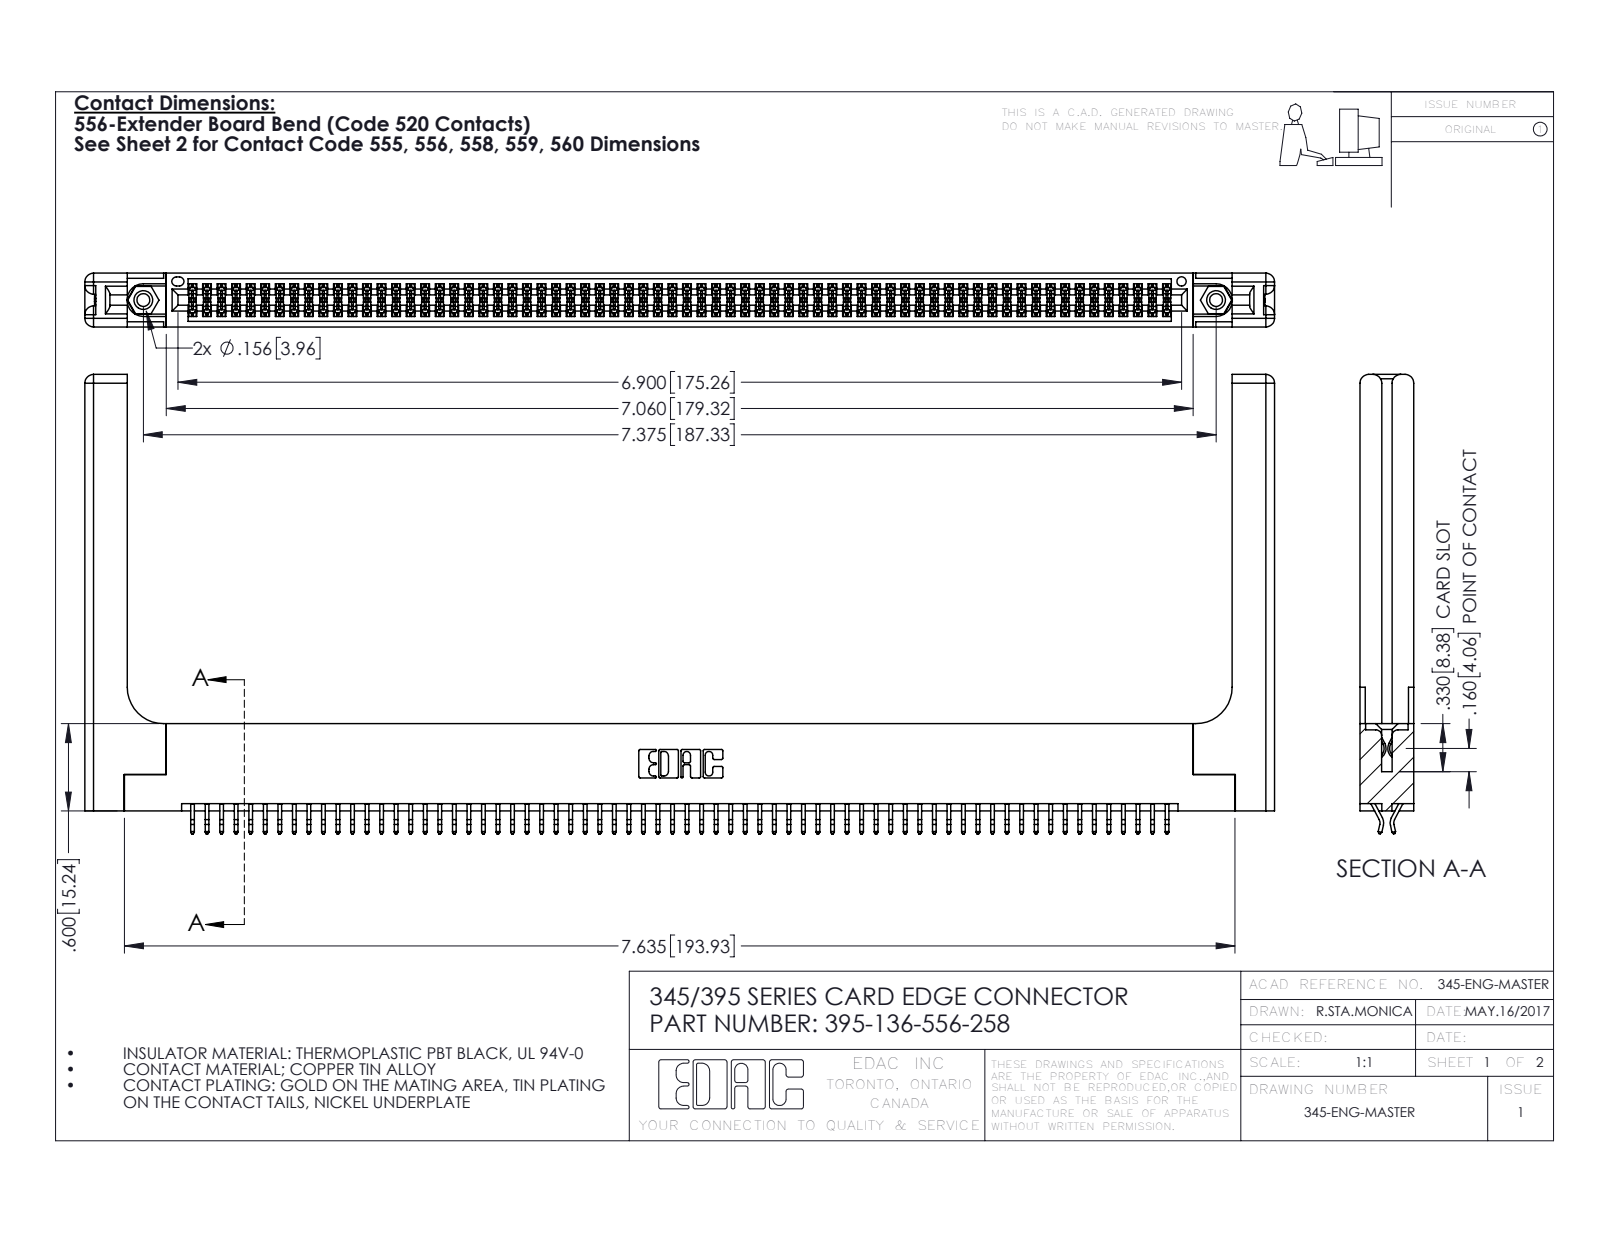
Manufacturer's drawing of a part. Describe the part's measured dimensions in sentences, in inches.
The part is named "345-220-058_345-220-058; 345 Part_Flush Mounting Lugs - 0.156 Dia-TH; 345-250-001_345-250-001-102; 345-292-001_556 Tail (+1 more)". Its 3-D file was written by "SolidWorks 2016 (CONFIG_CONTROL_DESIGN)". It is 141 solids with 7998 faces: 5260 planar, 2678 cylindrical and 60 other. Overall it measures 8.179 by 3.157 by 0.37 inches. Its volume is 1.763 cubic inches and its surface area 55.22 square inches. Round holes: 2 of diameter 0.089, 2 of diameter 0.125, 2 of diameter 0.156, 1 of diameter 0.064. Round bosses or shafts: 2 of diameter 0.155. Partial cylindrical surfaces (rounded edges, fillets, slot ends): 204 of radius 0.006, 22 of radius 0.01, 16 of radius 0.06, 6 of radius 0.007, 6 of radius 0.031, 3 of radius 0.026, 2 of radius 0.01, 2 of radius 0.014. The main face-to-face distances are 0.072, 0.298, 0.37, 0.2, 0.025, 0.098, 0.272, 0.225, 0.148, 0.15. The hole center spacings are 0.27, 7.139, 7.375.
